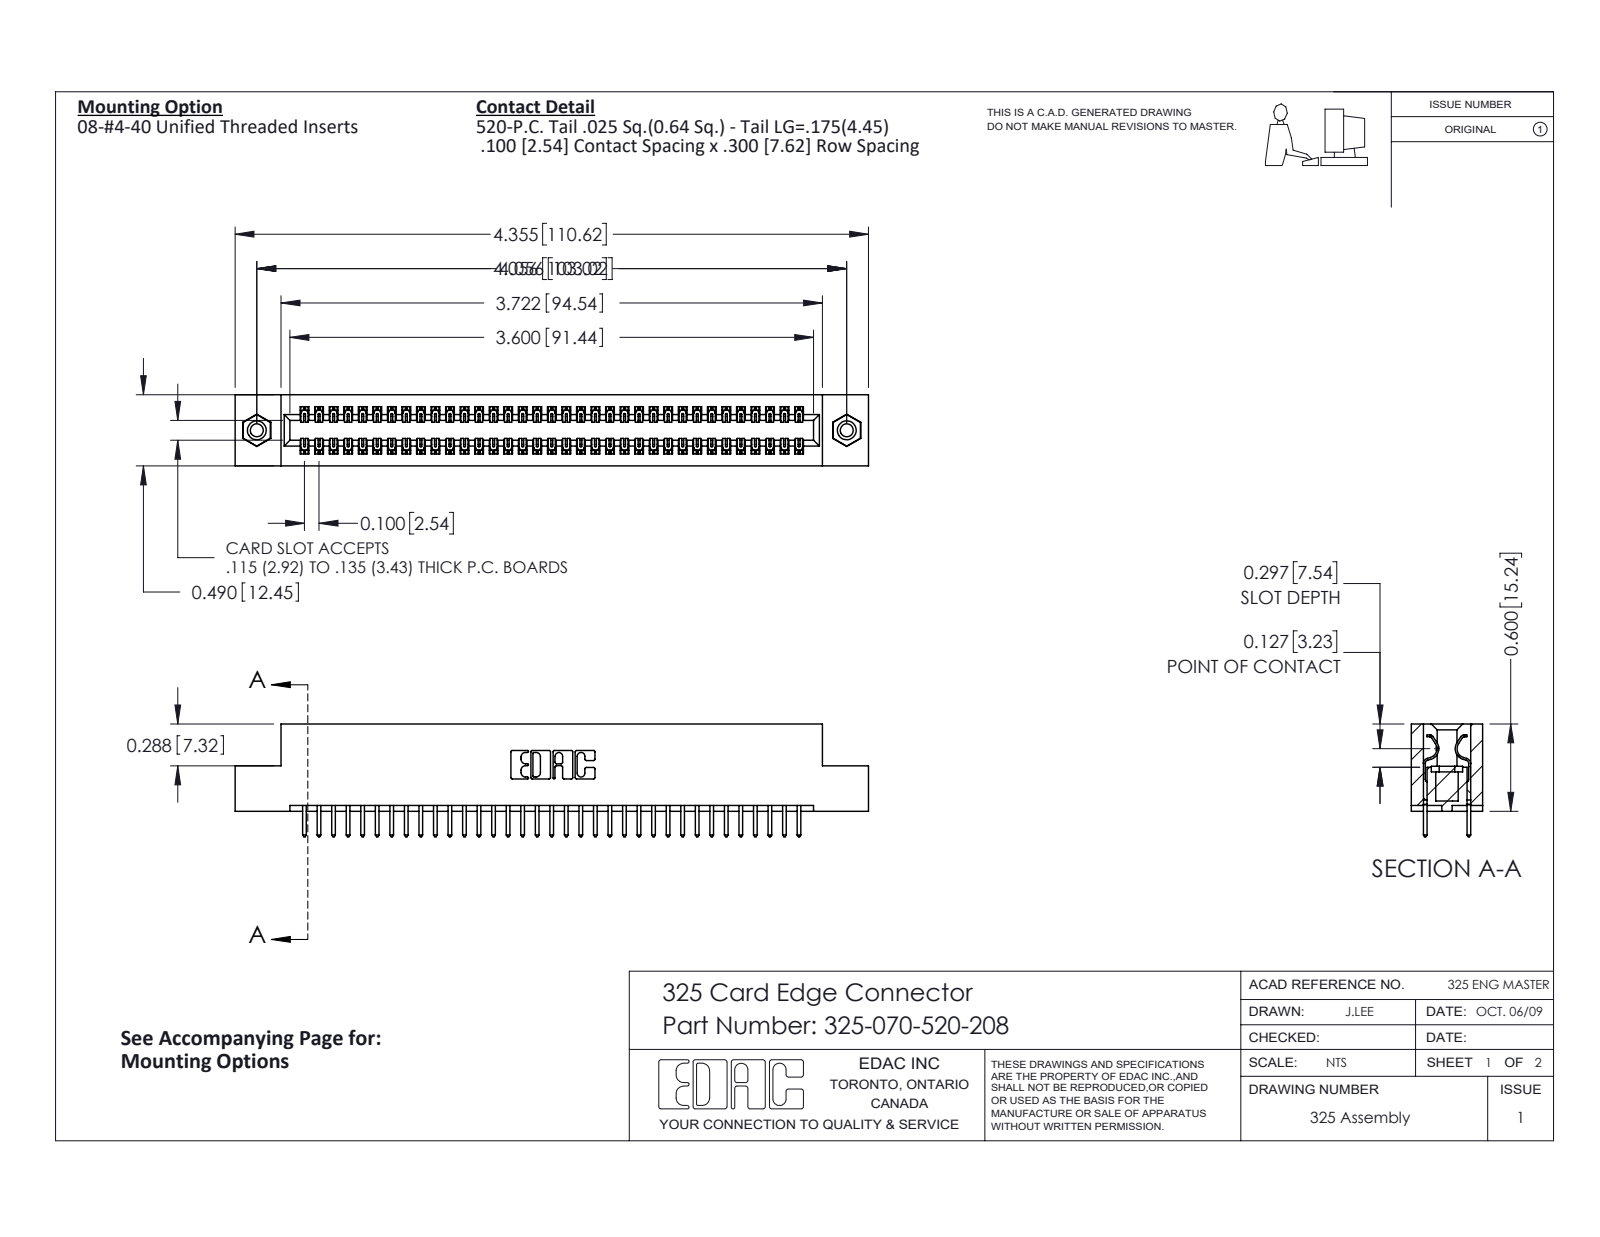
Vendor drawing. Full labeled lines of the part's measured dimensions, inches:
Part name (STEP PRODUCT): 325 Part_TI; 325-070-520-208; 345-250-001_345-250-003-102; 325-292-001_325-293-120
STEP written by: SolidWorks 2016 (CONFIG_CONTROL_DESIGN)
Units: inches
Bodies: 73 solids, 3814 faces (2622 planar, 1176 cylindrical, 16 other)
Overall size (bounding box): 4.355 × 0.775 × 0.49
Volume: 0.867 in³ · Surface area: 26.19 in²
Round holes (diameter × count): ⌀0.089 ×2, ⌀0.125 ×2, ⌀0.16 ×2
Round bosses / shafts (diameter × count): ⌀0.155 ×2
Partial cylindrical surfaces — rounded edges, fillets, slot ends (radius × count): R0.006 ×105, R0.01 ×70, R0.01 ×22, R0.007 ×6, R0.031 ×6, R0.026 ×3, R0.014 ×2, R0.022 ×2
Main face-to-face distances: 0.083, 0.407, 0.49, 0.3, 0.107, 0.383, 0.025, 0.325, 0.275, 0.56
Hole centre spacings: 4.056
